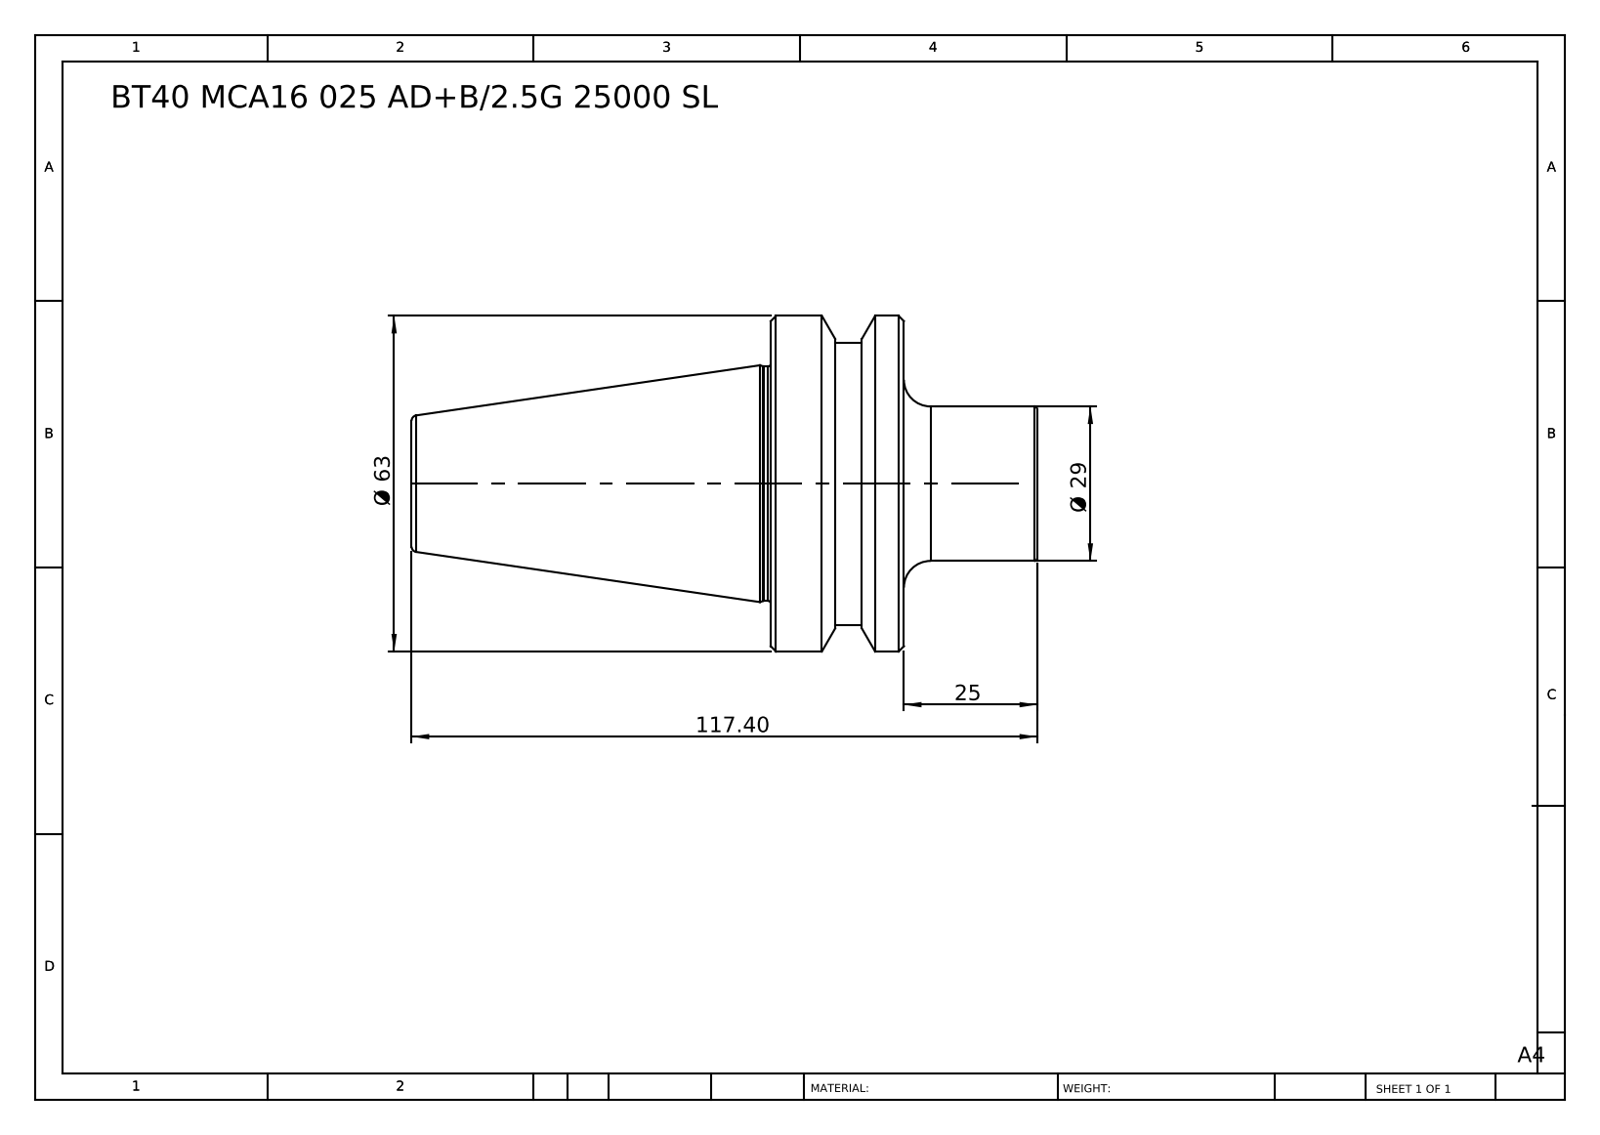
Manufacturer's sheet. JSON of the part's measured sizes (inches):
{"part_name": "BT40 MCA16 025 AD+B-2.5G 25000 SL", "step_written_by": "SolidWorks 2014 (CONFIG_CONTROL_DESIGN)", "units": "inches", "bodies": {"solids": 1, "faces": 38, "planar": 6, "cylindrical": 10, "other": 22}, "overall_size": [4.622, 2.48, 2.48], "volume_in3": 9.482, "surface_area_in2": 31.63, "round_bosses_or_shafts": [[2.48, 1], [2.087, 1], [1.732, 1], [1.142, 1]], "face_to_face_distances": [0.984, 1.969, 4.622, 3.638, 2.654, 1.492, 0.508, 0.476, 3.13, 1.295]}
